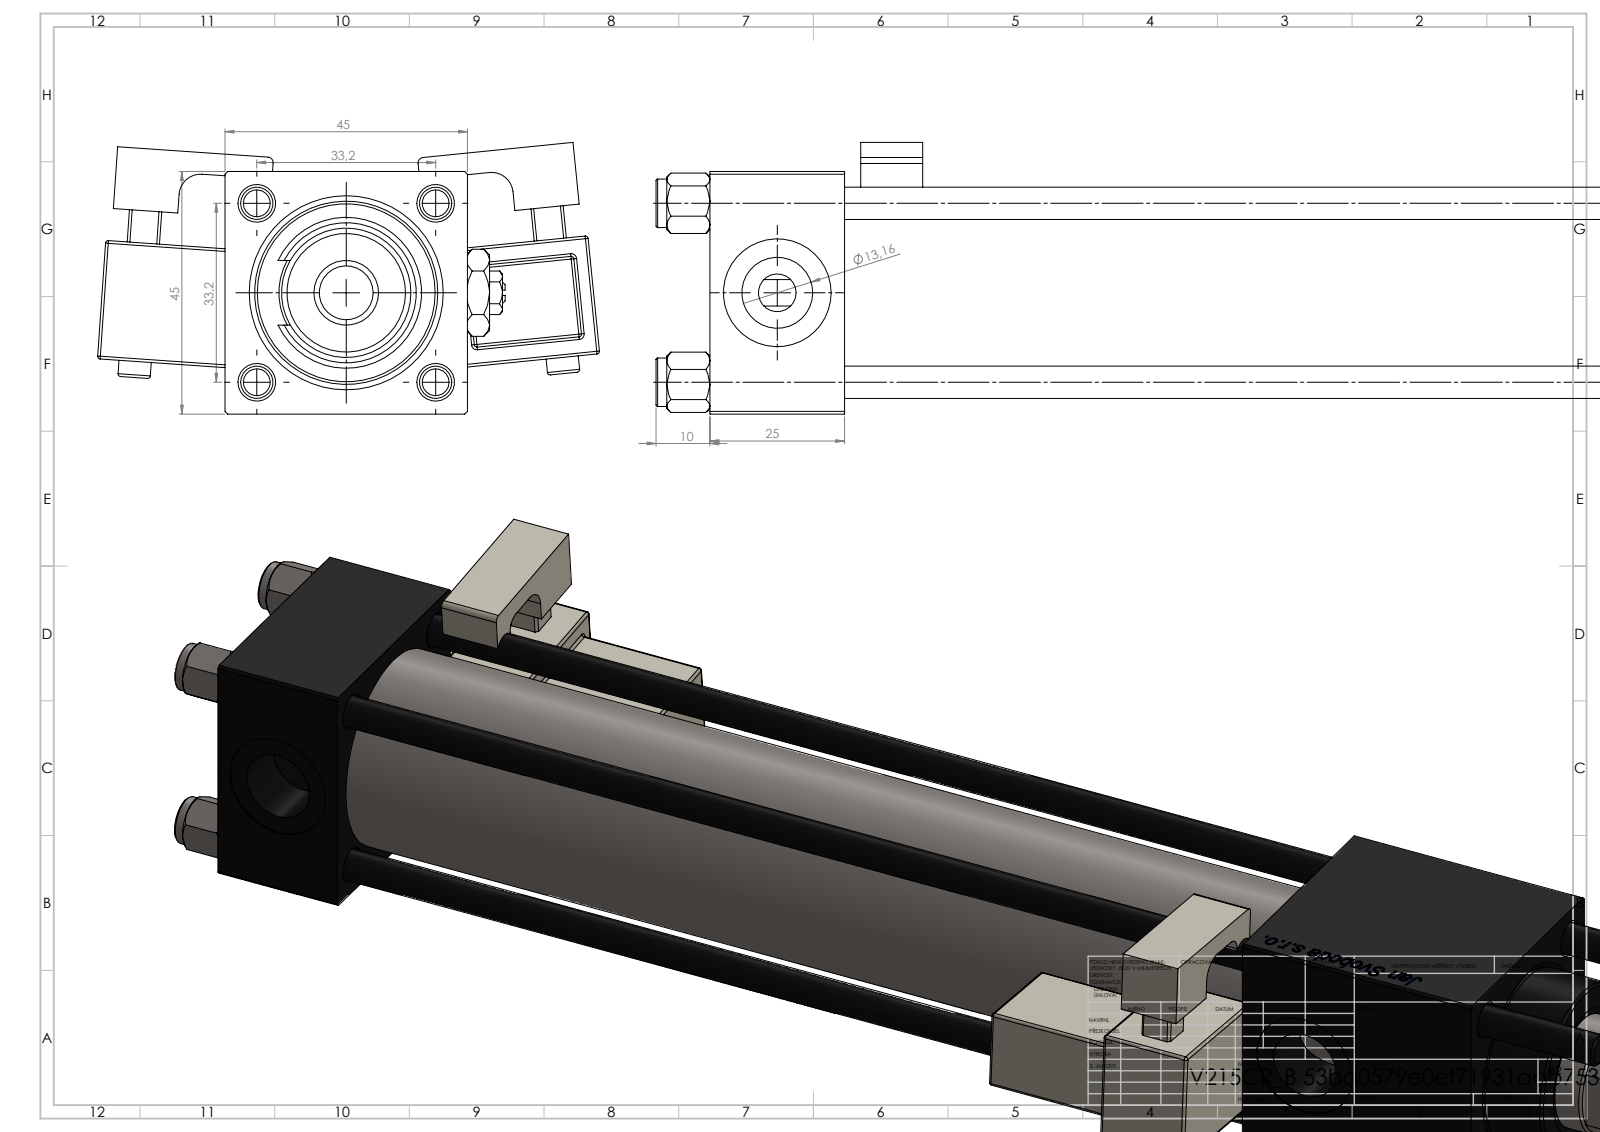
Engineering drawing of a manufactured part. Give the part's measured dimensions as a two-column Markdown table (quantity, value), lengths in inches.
| quantity | value |
| --- | --- |
| part name | V215CR_B_TYCINKA; V215CR_VCP_B; V215_VC_A; FEMALE_PART_FOR_DFA (+5 more) |
| STEP written by | SolidWorks 2019 (CONFIG_CONTROL_DESIGN) |
| units | inches |
| bodies | 17 solids, 1499 faces (568 planar, 161 cylindrical, 770 other) |
| overall size | 14.134 × 3.667 × 1.984 |
| volume | 23.59 in³ |
| surface area | 230.6 in² |
| round holes (diameter × count) | 0.236 × 4, 0.276 × 2, 0.518 × 2, 0.787 × 2, 0.413 × 1, 0.866 × 1, 0.945 × 1, 0.984 × 1, 1.26 × 1, 1.299 × 1 |
| round bosses / shafts (diameter × count) | 0.354 × 4, 0.236 × 2, 1.496 × 1, 1.339 × 1, 1.102 × 1, 0.709 × 1, 0.472 × 1, 0.433 × 1 |
| partial cylindrical surfaces (radius × count) | 0.02 × 48, 0.039 × 2, 0.098 × 2, 0.157 × 2, 0.384 × 1, 0.413 × 1 |
| main face-to-face distances | 1.772, 0.984, 8.465, 7.48, 0.118, 10.354, 0.571, 0.591, 6.791, 0.689 |
| hole center spacings | 0.924, 1.307, 1.848, 8.484 |
